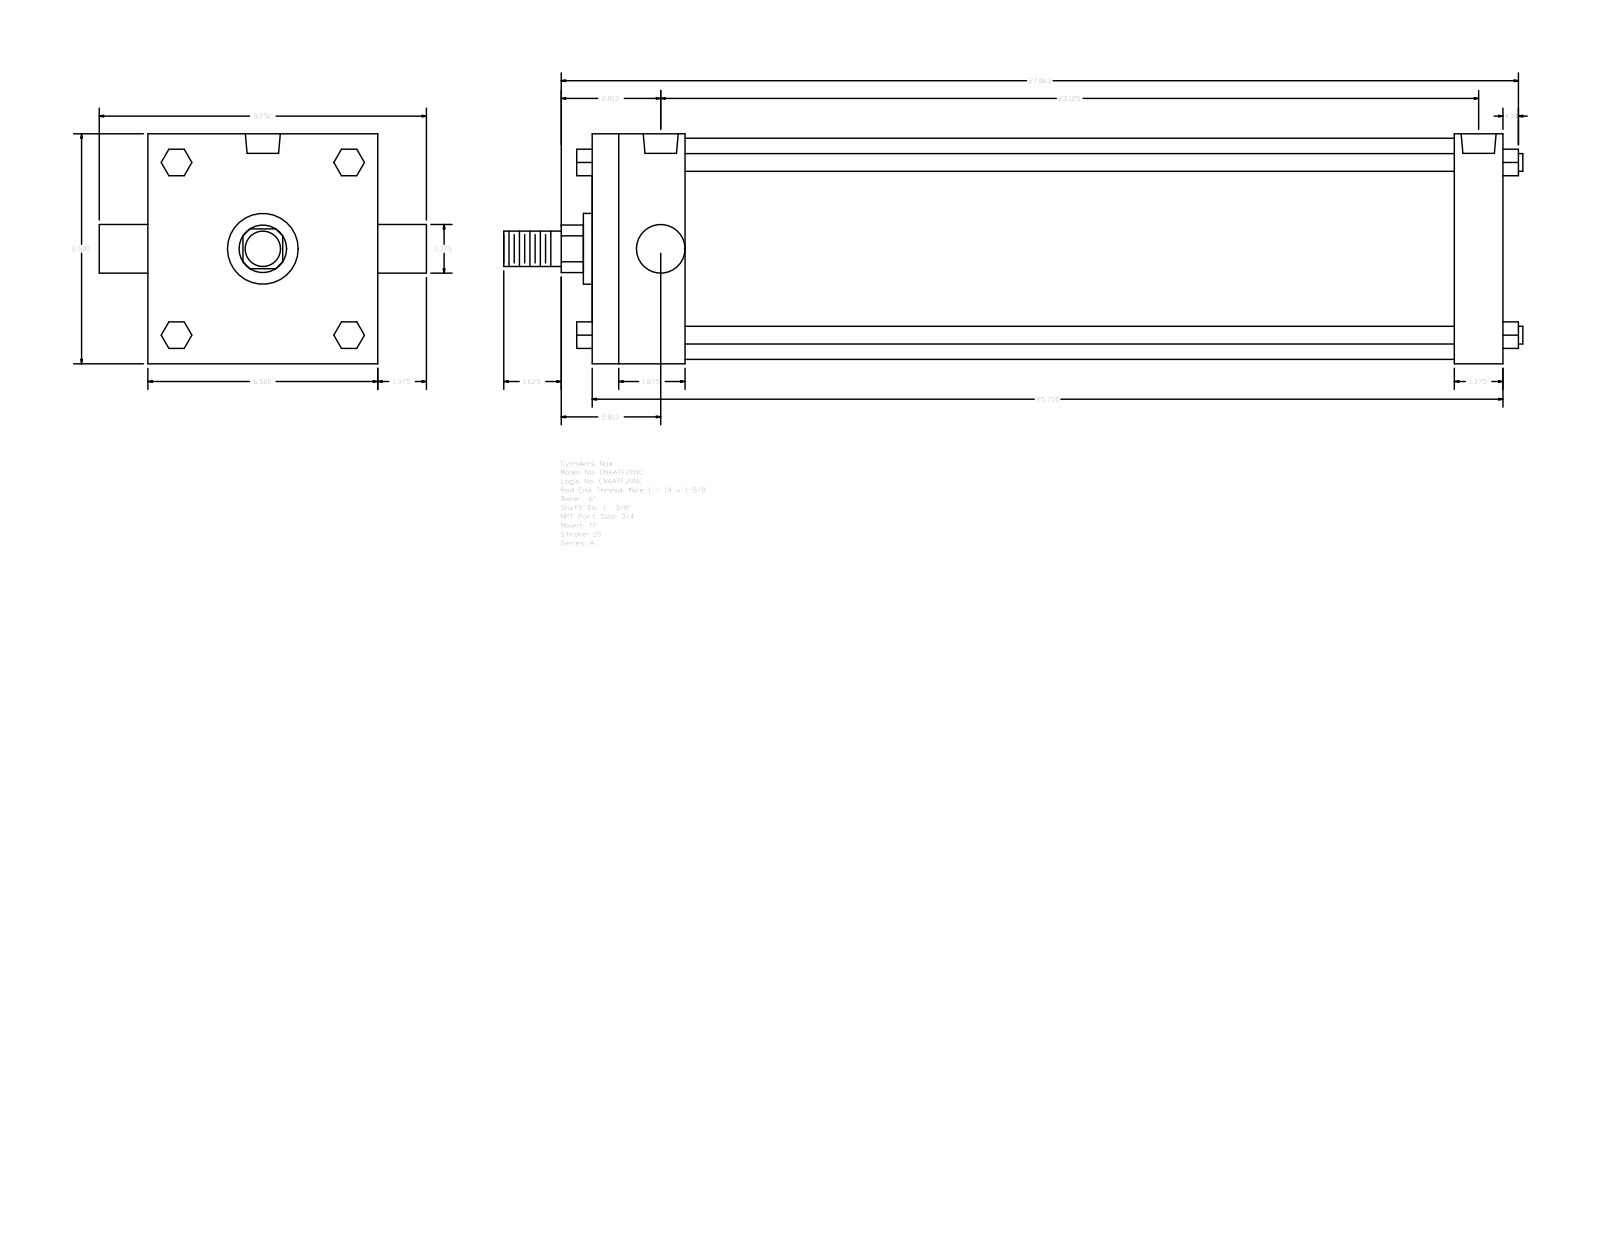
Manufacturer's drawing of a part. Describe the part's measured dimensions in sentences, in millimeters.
The part is named "A_TF__0600_1.375". Its 3-D file was written by "GSSL Pune (CONFIG_CONTROL_DESIGN)". It is 0 solids with 120 faces: 92 planar, 28 cylindrical and 0 other. Overall it measures 731.84 by 234.95 by 165.1 millimeters. Round holes: 3 of diameter 15.08, 2 of diameter 25.12. Round bosses or shafts: 4 of diameter 12.7, 2 of diameter 34.92, 1 of diameter 158.75, 1 of diameter 50.8, 1 of diameter 25.4. Partial cylindrical surfaces (rounded edges, fillets, slot ends): 1 of radius 17.06. The main face-to-face distances are 165.1, 654.04, 34.92, 66.67, 587.37, 619.12, 552.45, 19.05, 61.97, 107.34. The hole center spacings are 5.56, 581.81, 576.25, 587.37.
